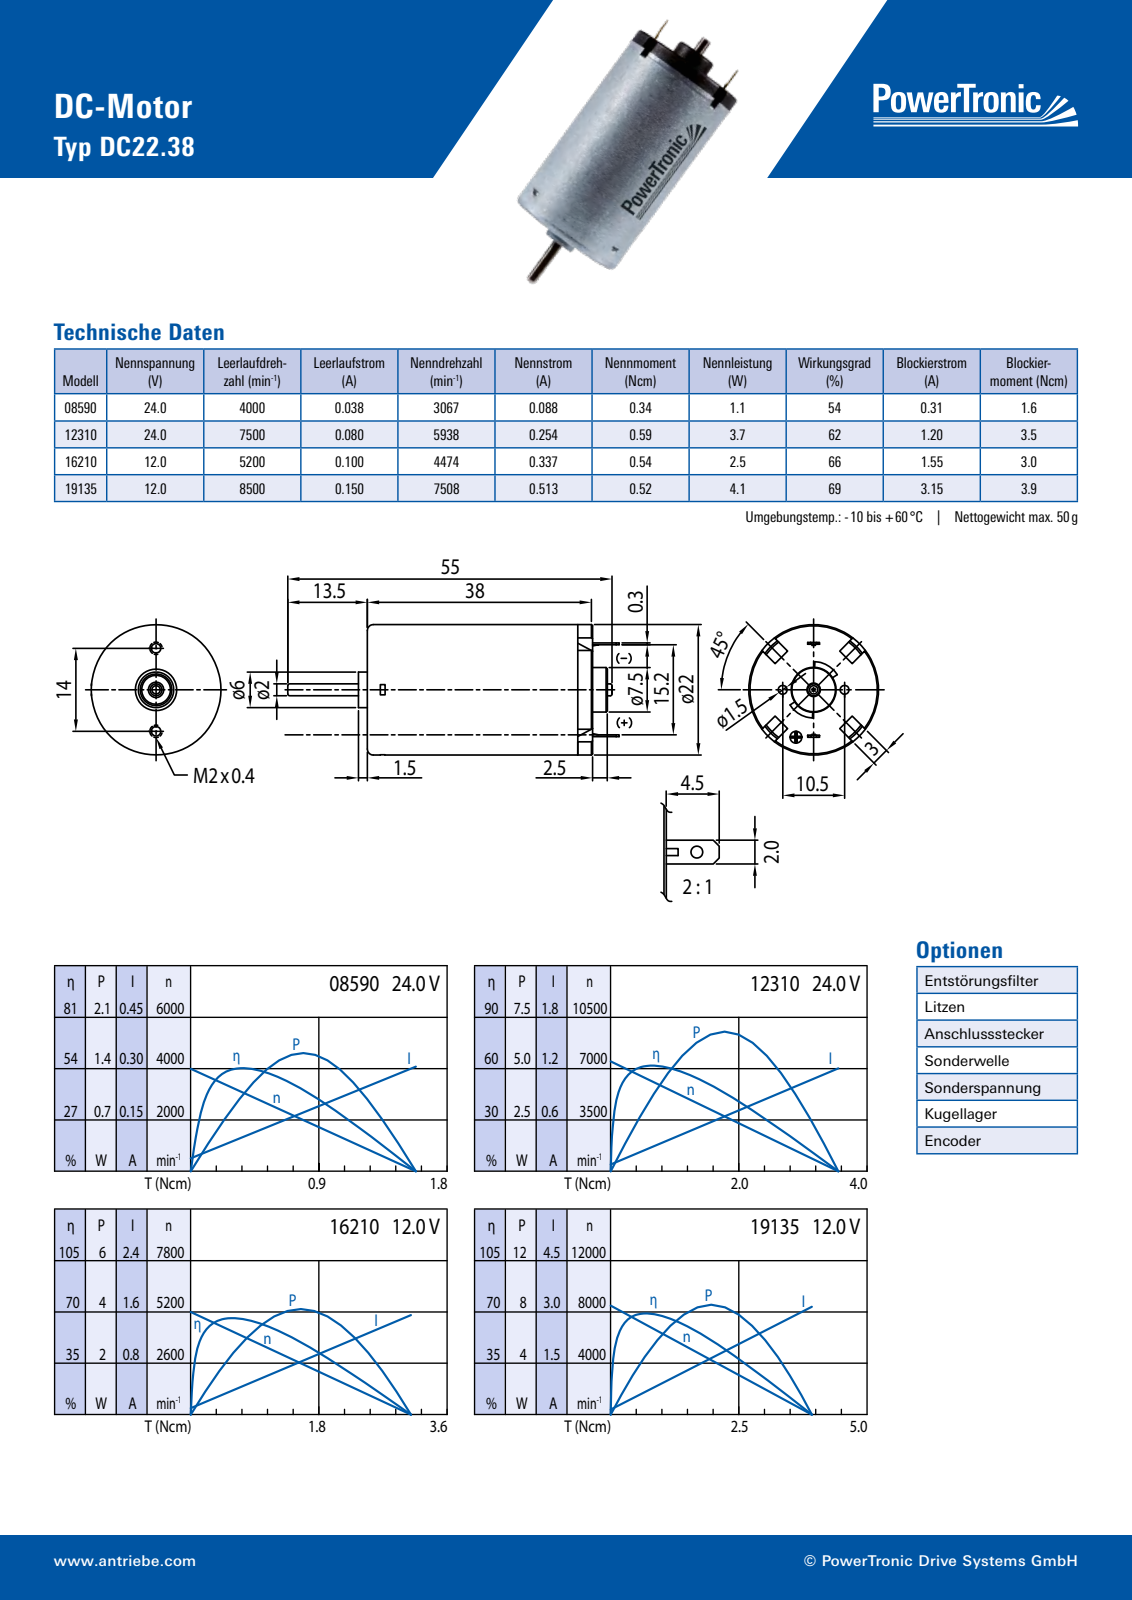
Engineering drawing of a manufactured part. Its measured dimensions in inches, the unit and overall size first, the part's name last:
Units: inches
Overall size (bounding box): 2.165 × 0.866 × 0.866
Round holes (diameter × count): ⌀0.028 ×4, ⌀0.031 ×4, ⌀0.079 ×3, ⌀0.051 ×2, ⌀0.063 ×2, ⌀0.076 ×1, ⌀0.077 ×1, ⌀0.078 ×1, ⌀0.087 ×1, ⌀0.089 ×1, ⌀0.177 ×1, ⌀0.205 ×1
Round bosses / shafts (diameter × count): ⌀0.866 ×1, ⌀0.813 ×1, ⌀0.809 ×1, ⌀0.795 ×1, ⌀0.591 ×1, ⌀0.335 ×1, ⌀0.295 ×1, ⌀0.23 ×1
Partial cylindrical surfaces — rounded edges, fillets, slot ends (radius × count): R0.008 ×12, R0.004 ×10, R0.012 ×10, R0.013 ×6, R0.016 ×6, R0.035 ×6, R0.079 ×6, R0.394 ×2
Main face-to-face distances: 1.496, 0.059, 0.028, 1.468, 0.098, 1.437, 0.039, 1.409, 0.118, 0.598
Hole centre spacings: 0.063, 0.078, 0.13, 0.352, 0.055, 0.076, 0.08, 0.128
Volume: 0.383 in³ · Surface area: 19.08 in²
Bodies: 37 solids, 769 faces (487 planar, 229 cylindrical, 53 other)
Part name (STEP PRODUCT): 17-R2500; 32-P1508; 13-0151; 21-13U00 (+8 more)
STEP written by: SolidWorks 2016 (CONFIG_CONTROL_DESIGN)
